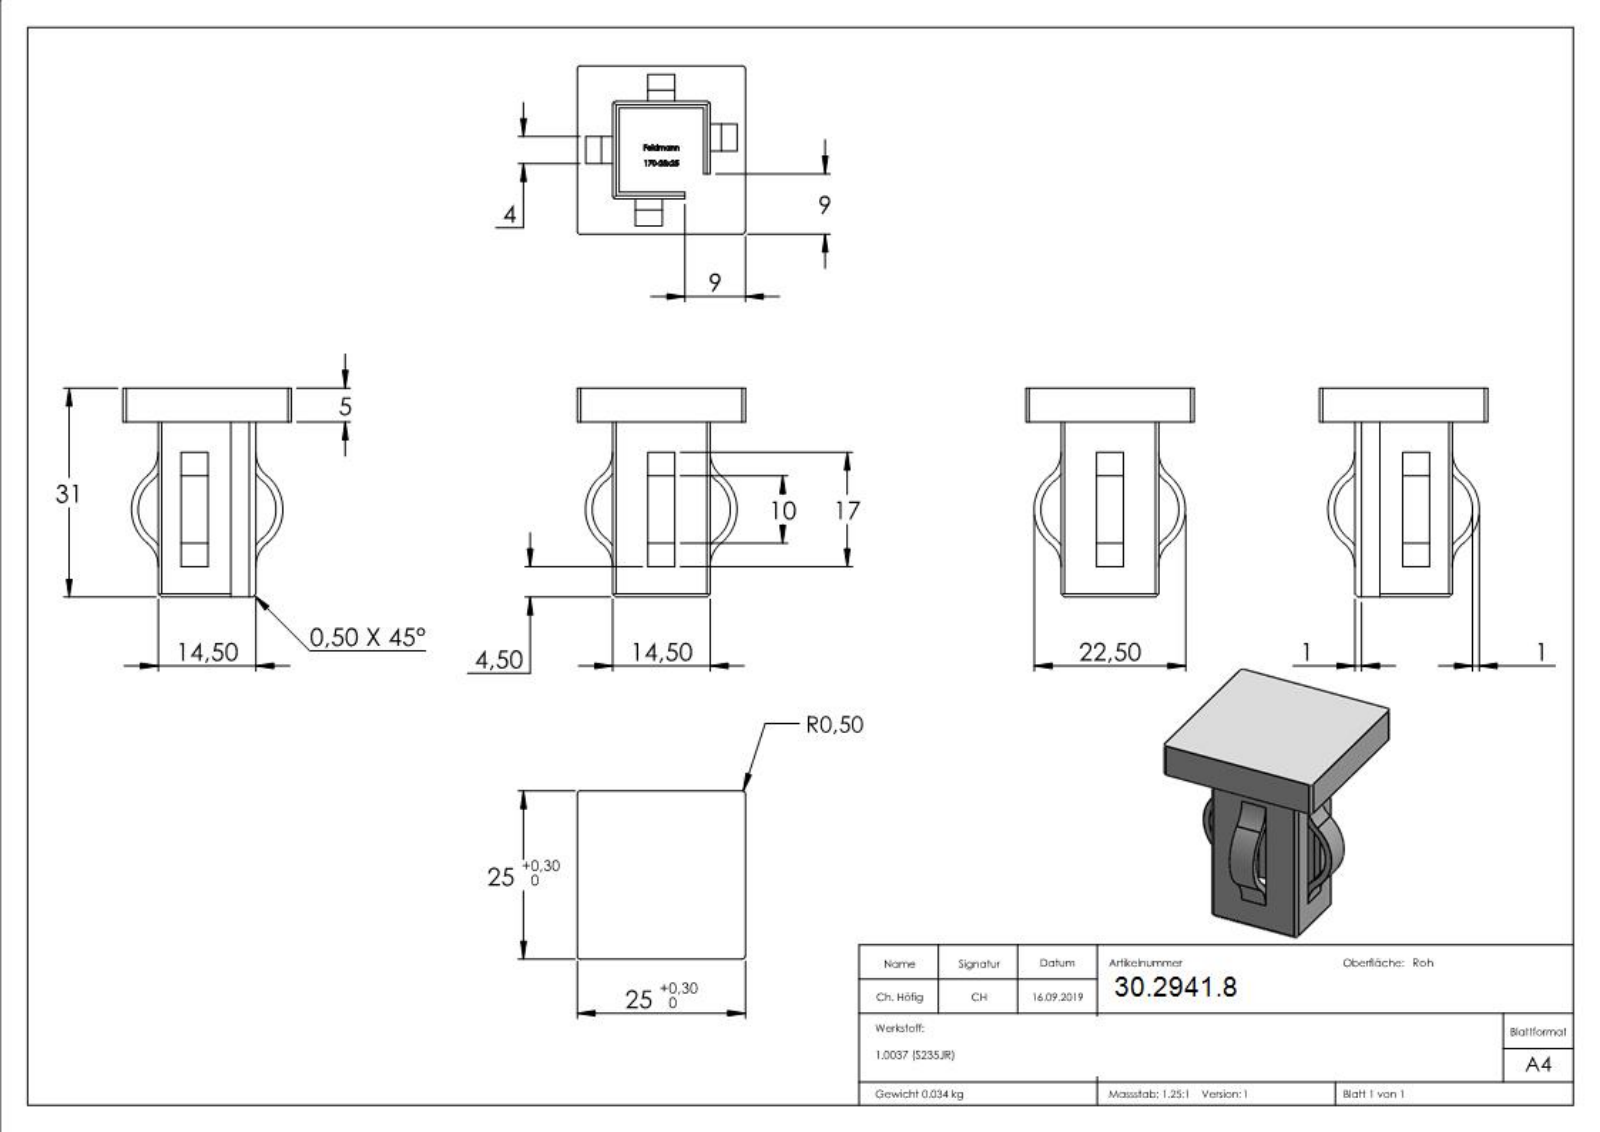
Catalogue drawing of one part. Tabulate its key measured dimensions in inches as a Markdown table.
| quantity | value |
| --- | --- |
| part name | 170-25x25 |
| STEP written by | SolidWorks 2015 (CONFIG_CONTROL_DESIGN) |
| units | inches |
| bodies | 1 solid, 284 faces (164 planar, 35 cylindrical, 85 other) |
| overall size | 1.22 × 0.984 × 0.984 |
| volume | 0.268 in³ |
| surface area | 7.042 in² |
| partial cylindrical surfaces (radius × count) | 0.02 × 7, 0.179 × 4, 0.218 × 4, 0.22 × 4, 0.259 × 4, 0.216 × 2, 0.227 × 2, 0.256 × 2 |
| main face-to-face distances | 0.039, 0.531, 0.207, 0.197, 0.571, 0.246, 0.738, 0.778, 0.492, 0.984 |
